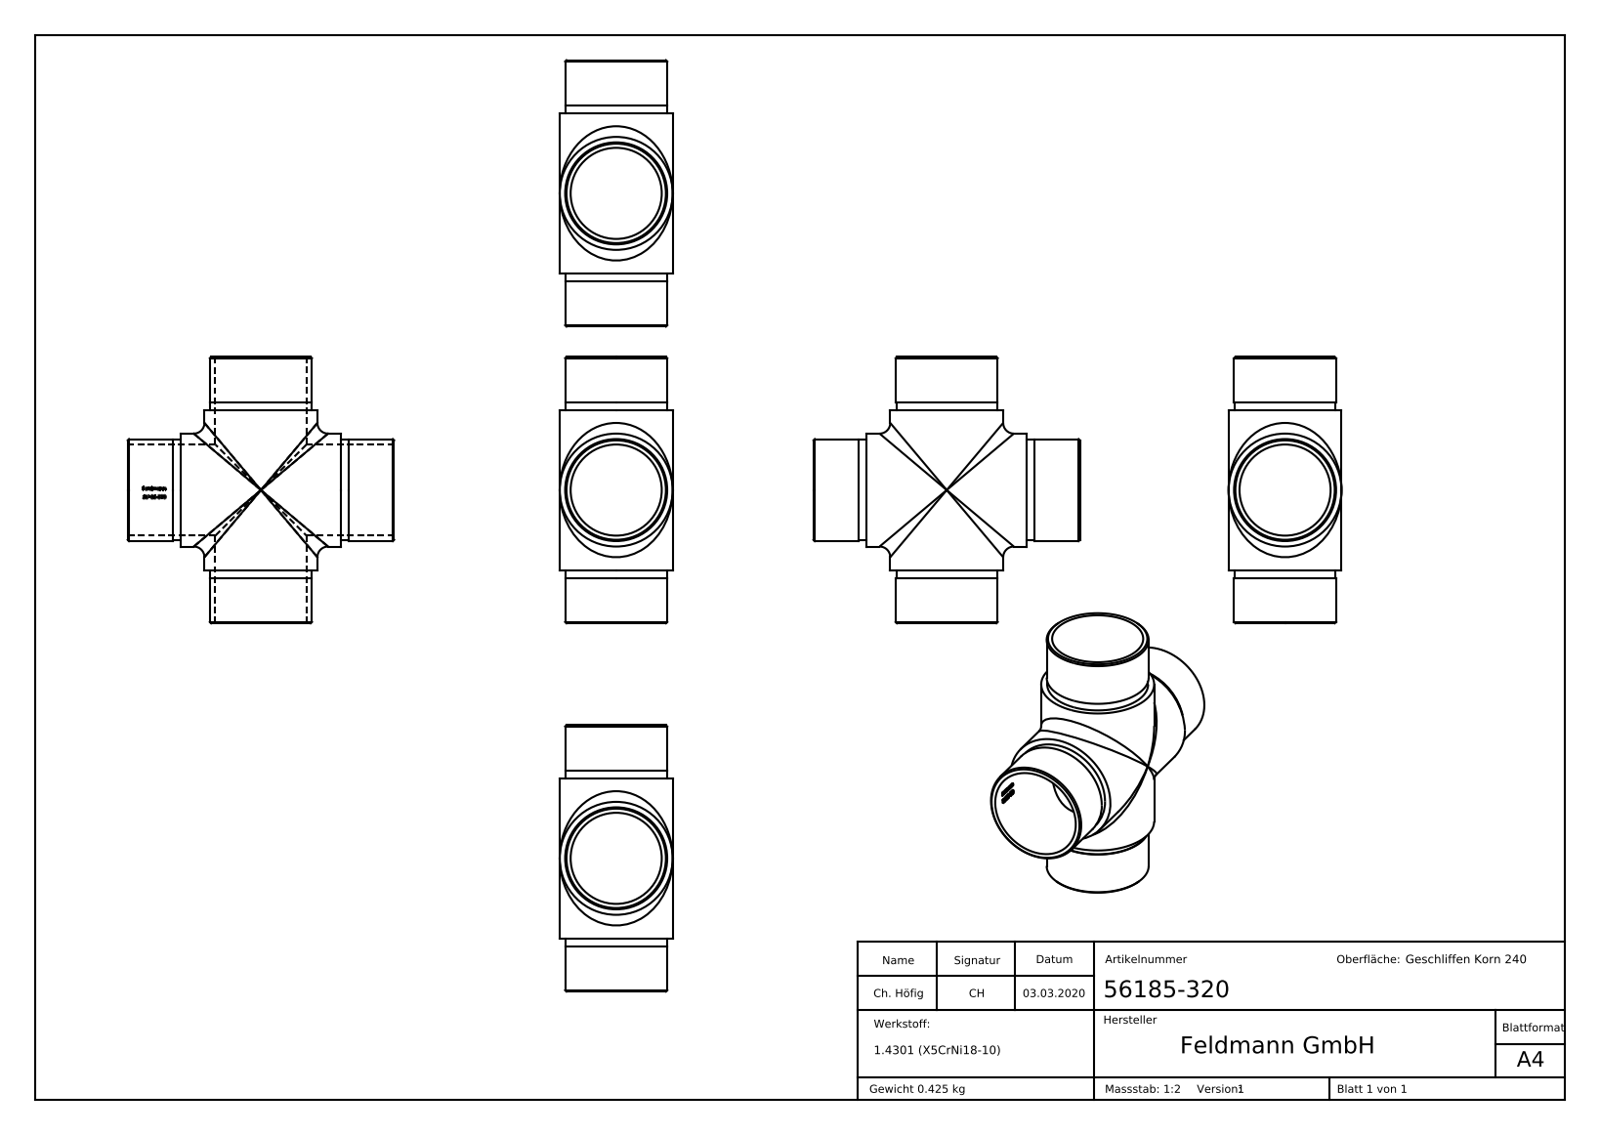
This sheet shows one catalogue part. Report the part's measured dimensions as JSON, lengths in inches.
{"part_name": "56185-320", "step_written_by": "SolidWorks 2015 (CONFIG_CONTROL_DESIGN)", "units": "inches", "bodies": {"solids": 1, "faces": 267, "planar": 100, "cylindrical": 40, "other": 127}, "overall_size": [3.937, 3.937, 1.669], "volume_in3": 3.28, "surface_area_in2": 57.48, "round_holes": [[1.346, 2]], "round_bosses_or_shafts": [[1.669, 2], [1.508, 2], [1.492, 2]], "partial_cylinders_radius": [[0.677, 1]], "face_to_face_distances": [0.787, 3.15, 2.362, 3.937, 0.669, 3.268, 0.118, 2.48, 2.598, 0.015]}
